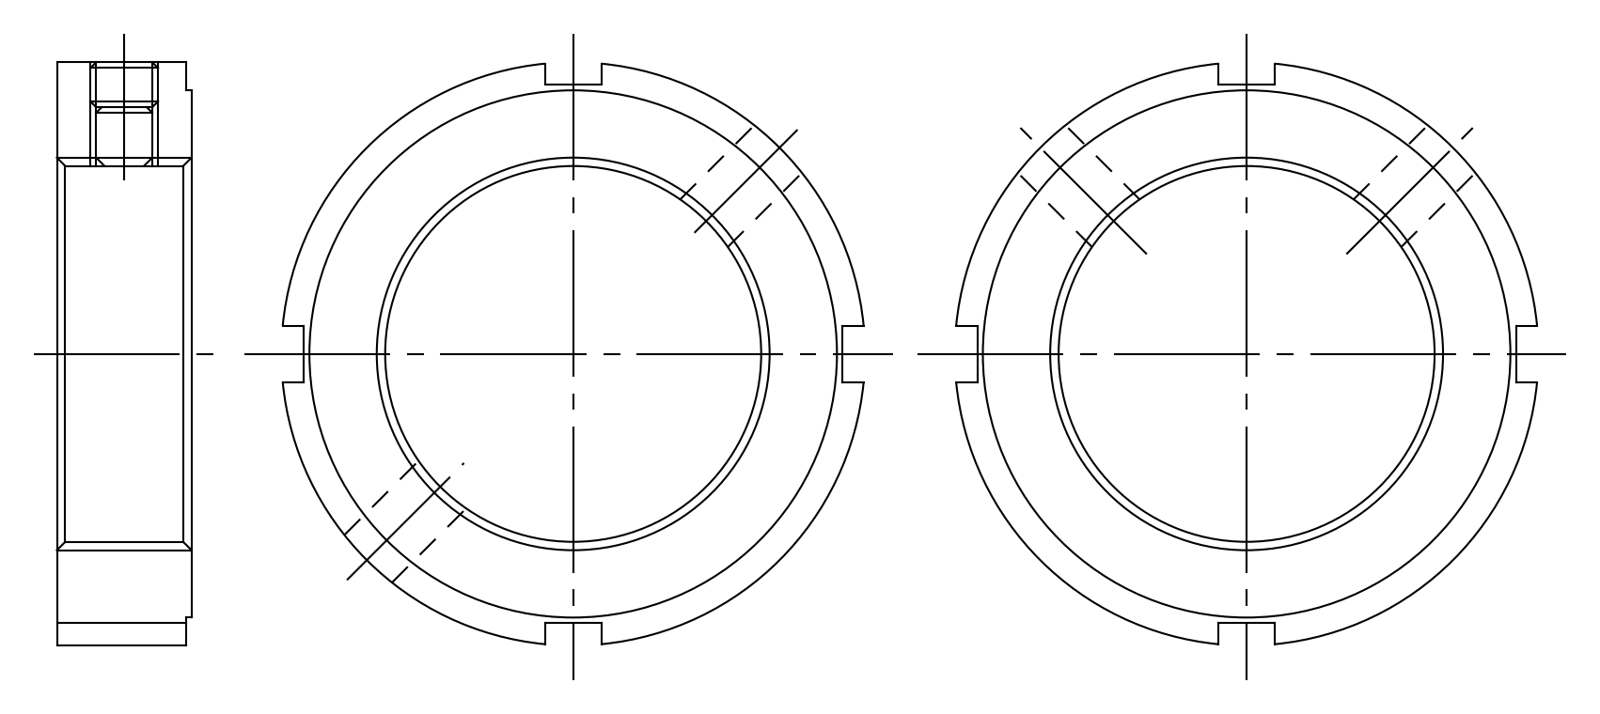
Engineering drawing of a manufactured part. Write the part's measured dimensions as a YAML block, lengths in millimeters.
part_name: "FKD ZM 35"
step_written_by: "Autodesk Inventor 2011 (AUTOMOTIVE_DESIGN)"
units: millimeters
bodies: {solids: 1, faces: 23, planar: 15, cylindrical: 8, other: 0}
overall_size: [51.76, 51.76, 12]
volume: 12971
surface_area: 5877
round_holes:
  - {diameter: 4.92, count: 2}
  - {diameter: 35, count: 1}
round_bosses_or_shafts:
  - {diameter: 52, count: 1}
  - {diameter: 47, count: 1}
face_to_face_distances: [12, 0.5, 11.5, 21.5, 26.5, 48, 5]
